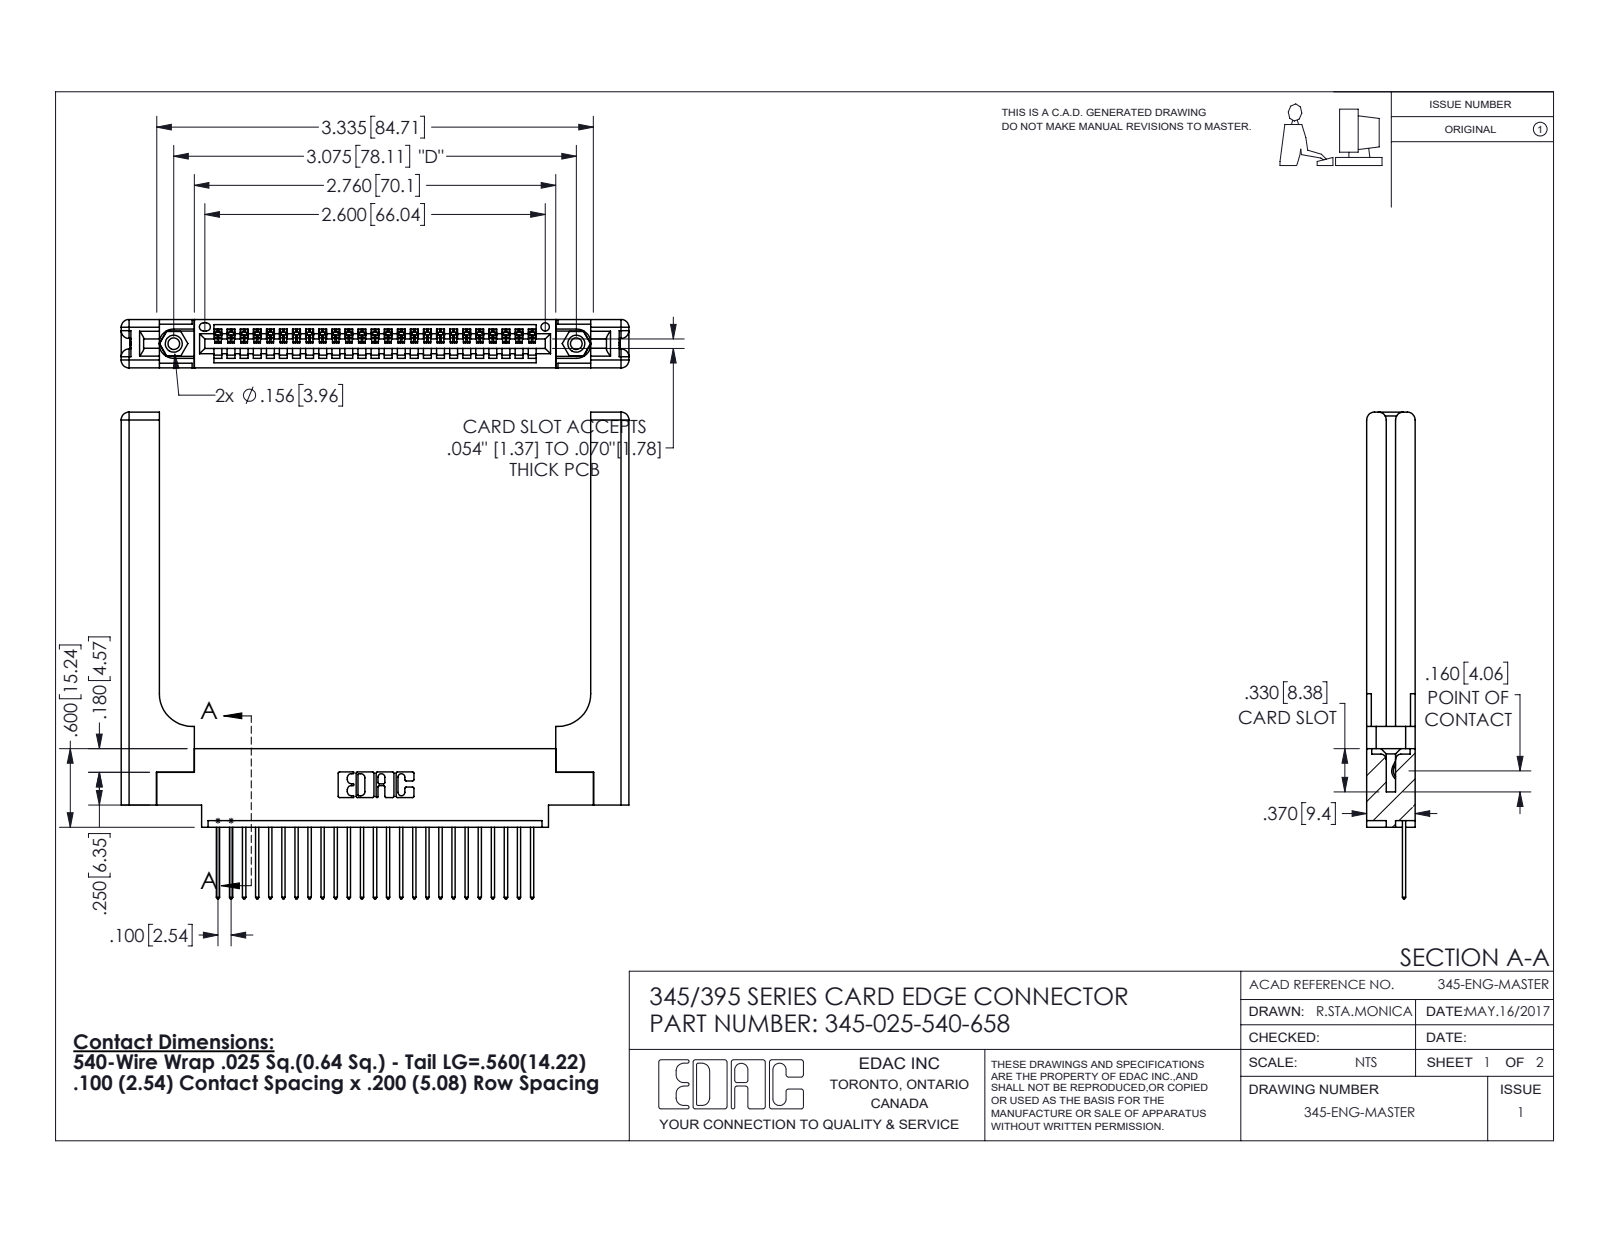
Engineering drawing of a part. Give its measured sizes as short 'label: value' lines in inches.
name: 345-250-001_345-250-001-102; 345 Part_0.170 Offset - 0.156 Dia-TH; 345-220-058_345-220-058; 345-025-540-658 (+1 more)
written by: SolidWorks 2016 (CONFIG_CONTROL_DESIGN)
unit: in
bodies: 30 solids, 1836 faces (1232 planar, 544 cylindrical, 60 other)
size: 3.879 × 3.717 × 0.37
volume: 1.077 in³; area: 27.26 in²
holes: 2× ⌀0.089, 2× ⌀0.125, 2× ⌀0.156, 1× ⌀0.064
bosses: 2× ⌀0.155
rounds: 50× R0.006, 50× R0.01, 22× R0.01, 16× R0.06, 6× R0.007, 6× R0.031, 3× R0.026, 2× R0.03
face distances: 0.37, 0.072, 0.298, 0.098, 0.272, 0.025, 0.148, 0.15, 0.2, 0.077
hole spacings: 0.27, 2.84, 3.075
